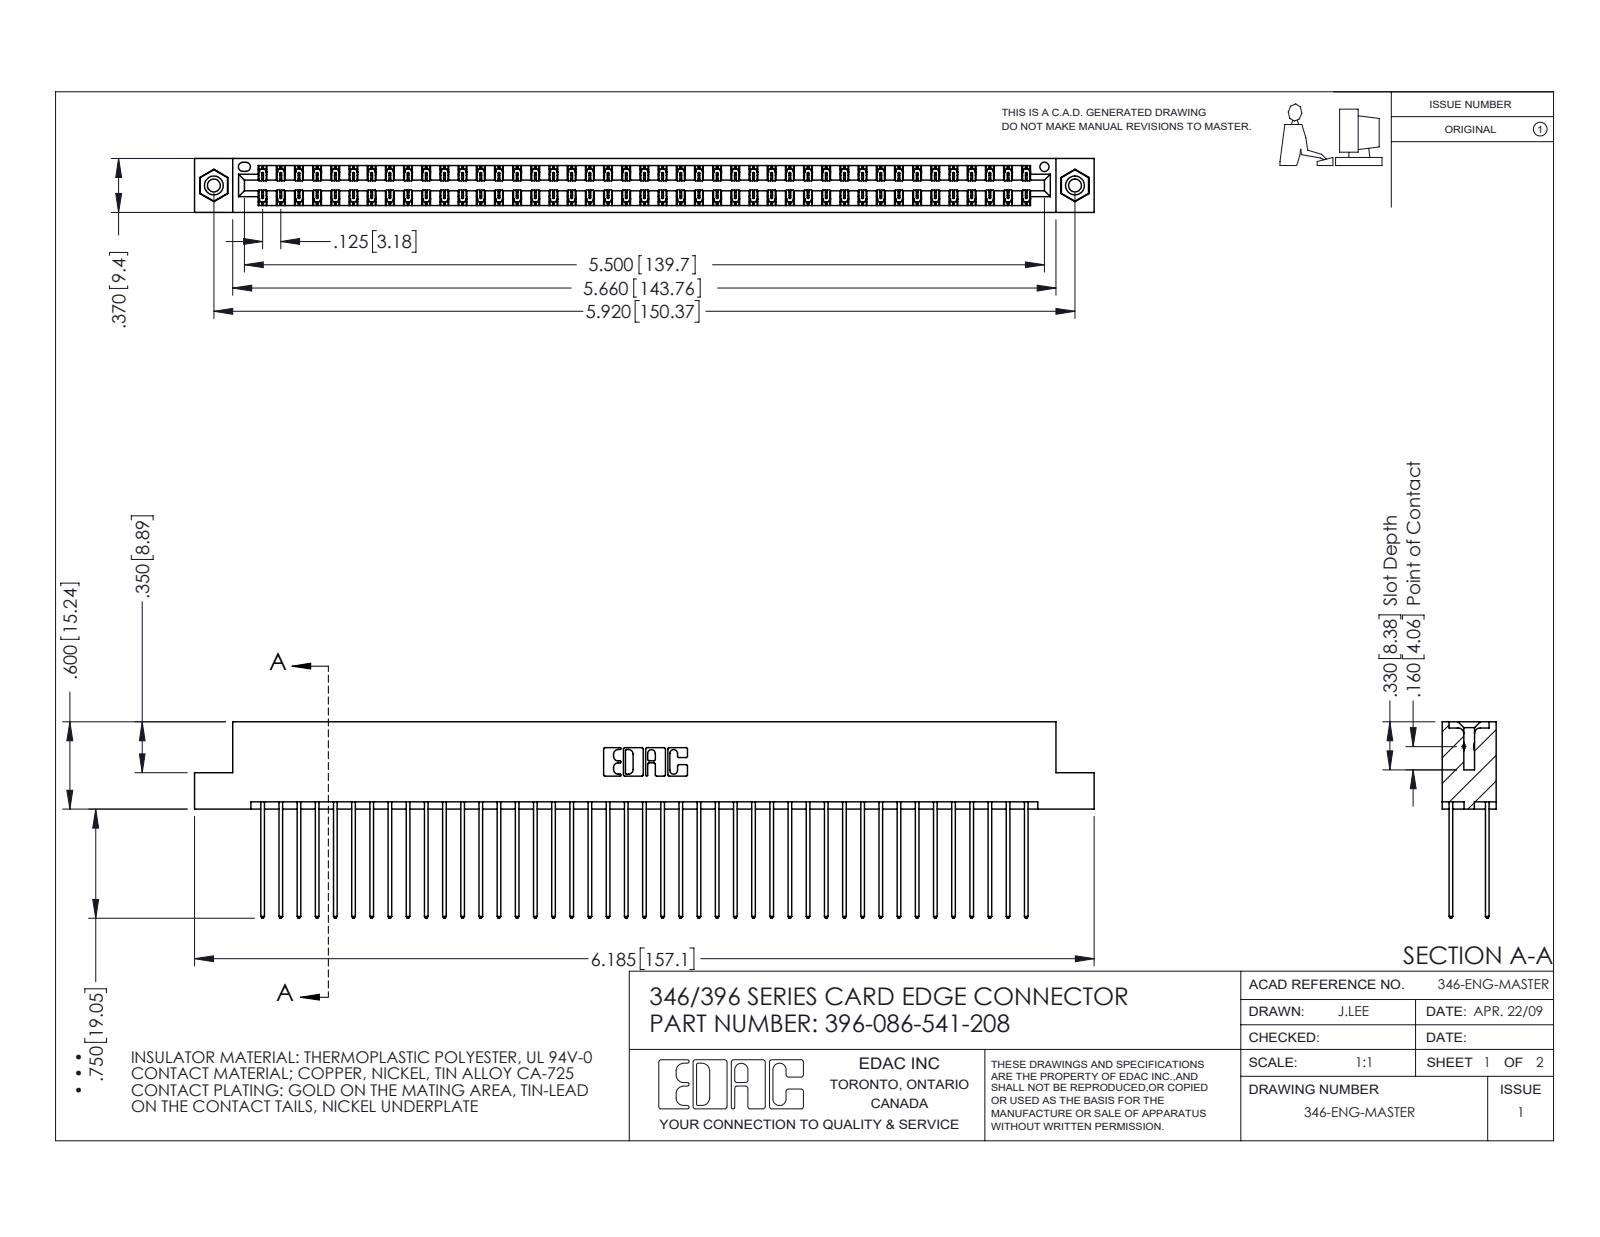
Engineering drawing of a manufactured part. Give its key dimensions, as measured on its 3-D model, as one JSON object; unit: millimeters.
{"part_name": "346 Part_Flush Mounting Lugs - 0.156 Dia-TI; 345-292-001_345-293-141; 345-250-001_345-250-003-102; 396-086-541-208", "step_written_by": "SolidWorks 2016 (CONFIG_CONTROL_DESIGN)", "units": "millimeters", "bodies": {"solids": 89, "faces": 4654, "planar": 3118, "cylindrical": 1520, "other": 16}, "overall_size": [157.1, 34.3, 9.4], "volume_mm3": 15800, "surface_area_mm2": 24140, "round_holes": [[2.3, 2], [3.2, 2], [4, 2], [1.6, 1]], "round_bosses_or_shafts": [[3.9, 2]], "partial_cylinders_radius": [[0.2, 129], [0.3, 86], [0.3, 22], [0.2, 6], [0.8, 6], [0.7, 3], [0.4, 2], [0.6, 2]], "face_to_face_distances": [1.2, 8.2, 6.4, 1.8, 7.6, 0.6, 9.4, 7, 5.7, 3.8], "hole_center_spacings": [6.2, 145.1, 150.4]}
